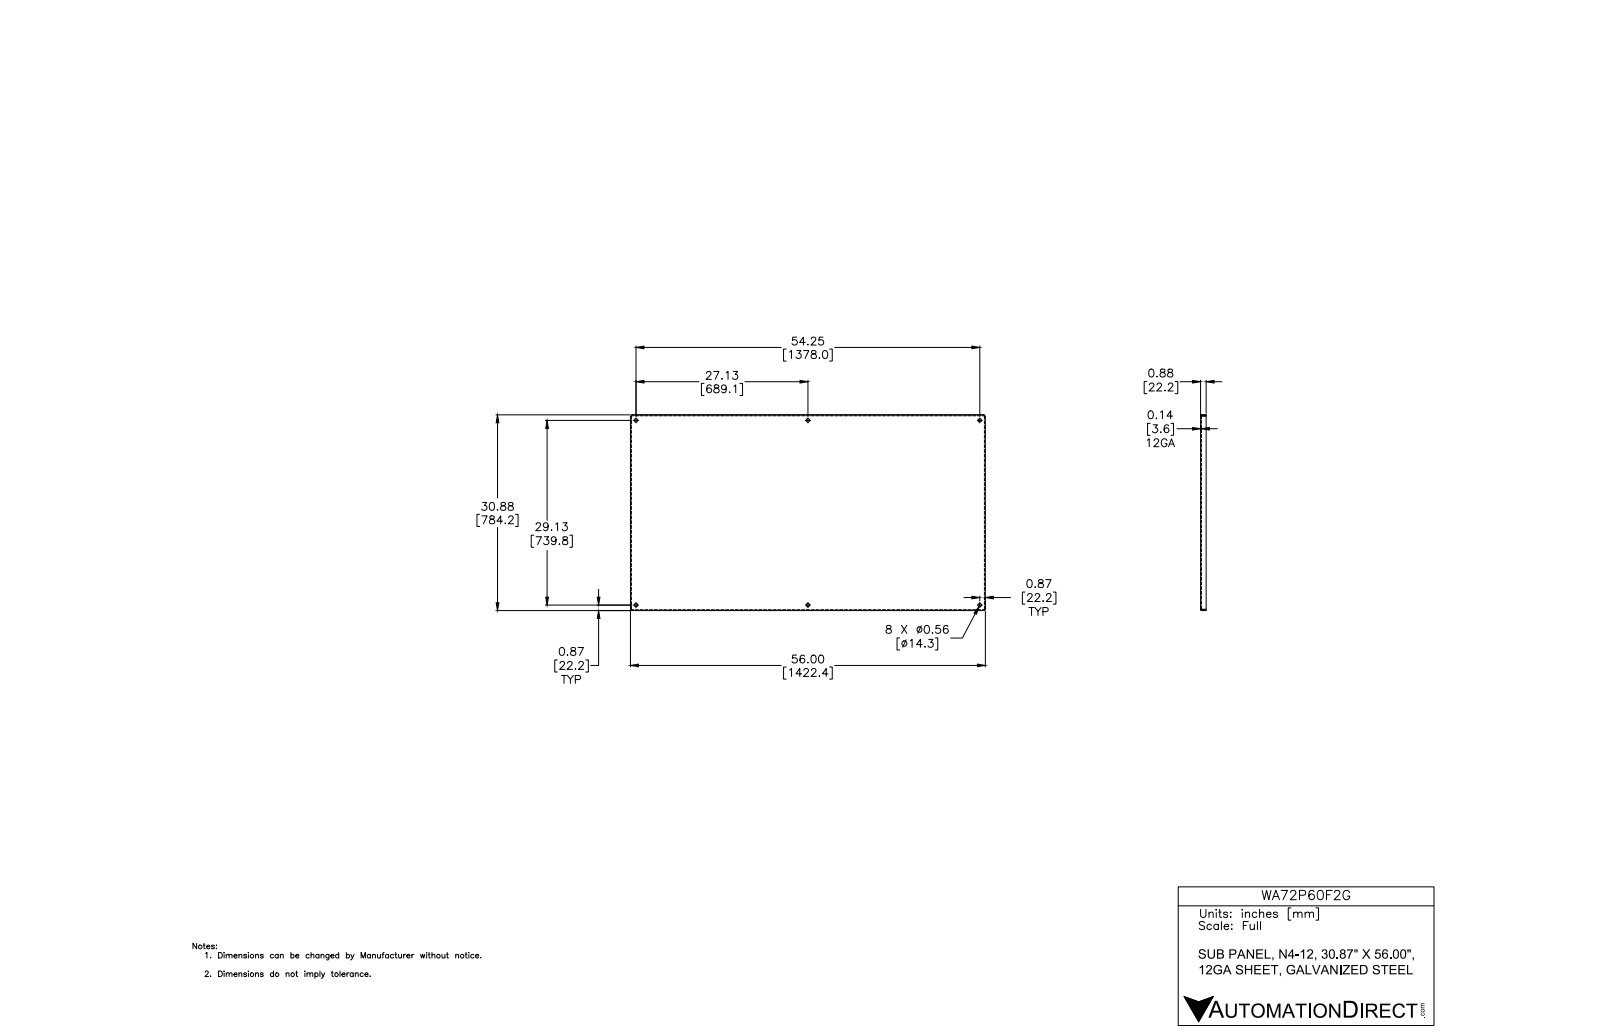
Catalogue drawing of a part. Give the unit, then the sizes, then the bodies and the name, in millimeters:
Units: millimetres
Overall size (bounding box): 1422.4 × 784.4 × 22.2
Round holes (diameter × count): ⌀14.3 ×6
Partial cylindrical surfaces — rounded edges, fillets, slot ends (radius × count): R0.4 ×4, R3.6 ×4
Main face-to-face distances: 3.2, 3.2, 784.4, 781.2, 781.2, 778, 1422.4, 1419.2, 1419.2, 1416.1
Hole centre spacings: 689, 739.9, 1011, 1011, 1378, 1564, 739.9
Volume: 3 792 000 mm³ · Surface area: 2 404 000 mm²
Bodies: 1 solid, 44 faces (22 planar, 14 cylindrical, 8 other)
Part name (STEP PRODUCT): WA_P_F_G
STEP written by: Autodesk Inventor 2012 (AUTOMOTIVE_DESIGN)
